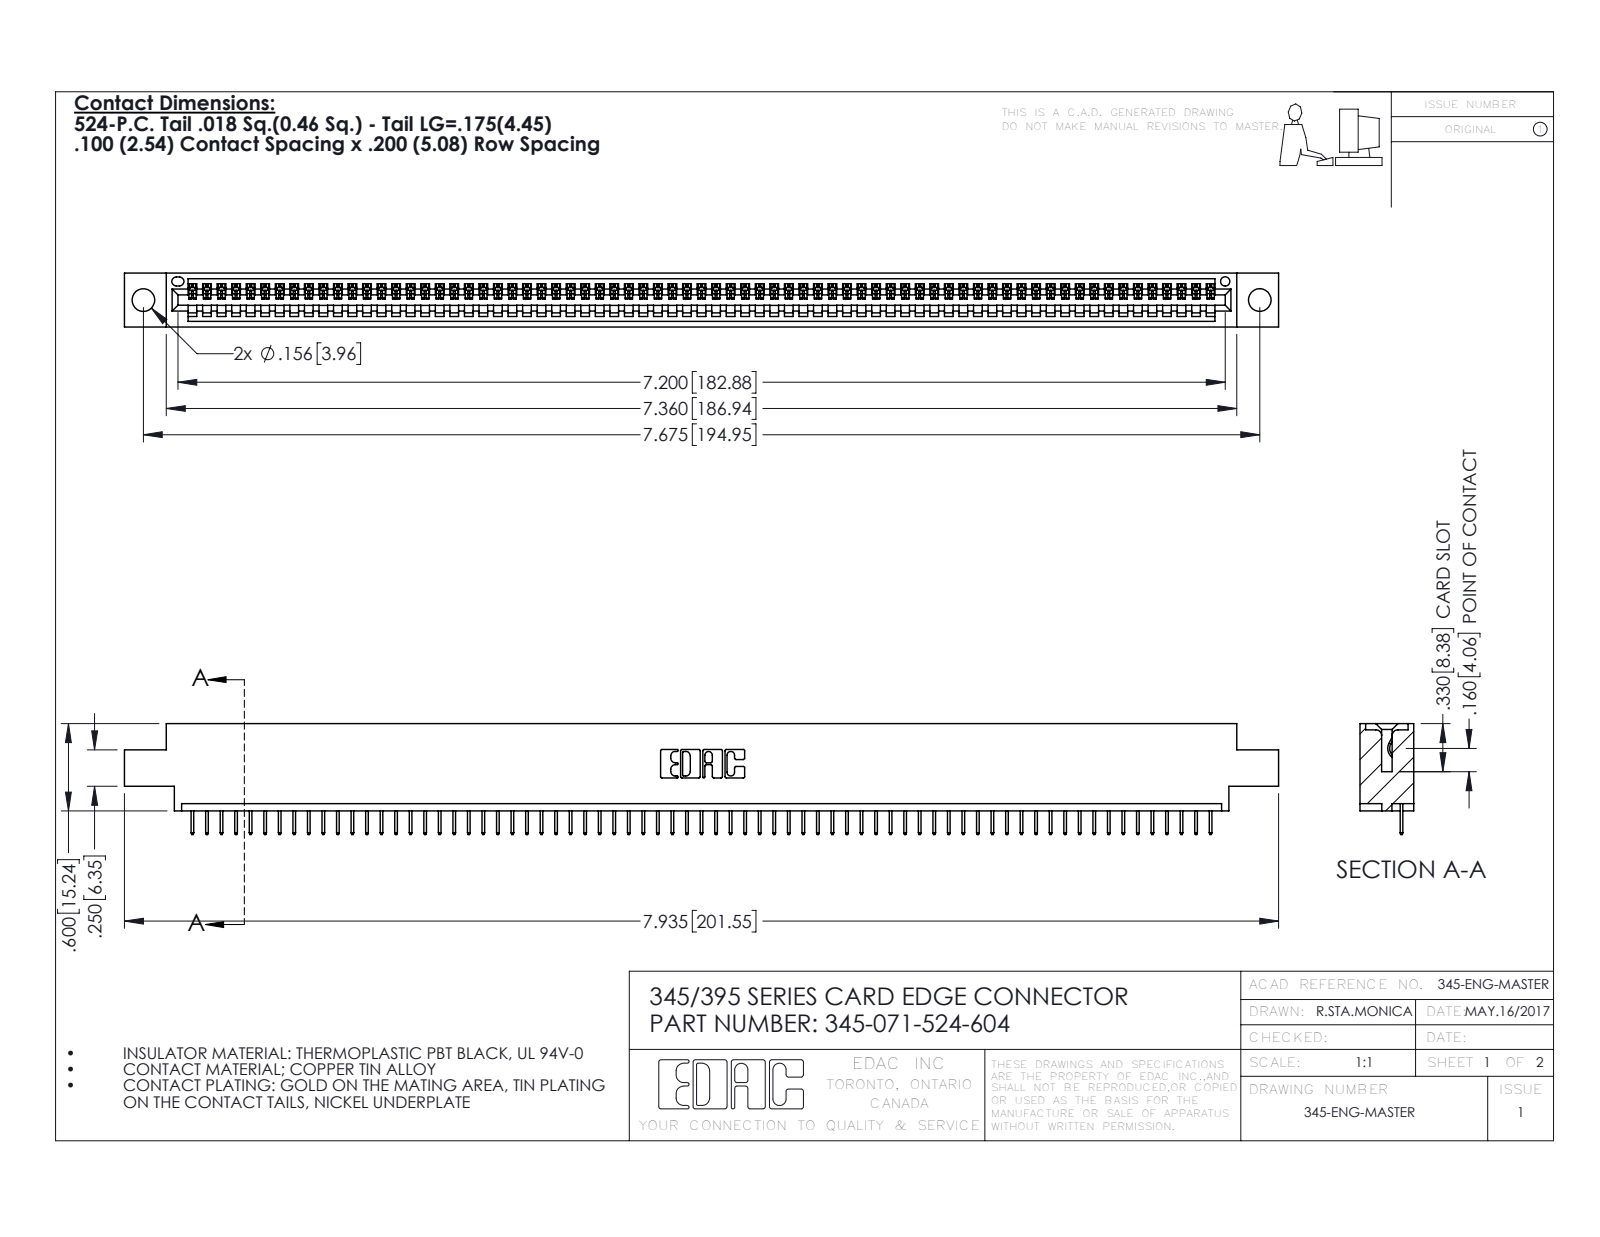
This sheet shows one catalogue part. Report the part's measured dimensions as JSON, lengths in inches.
{"part_name": "345-071-524-604; 345-292-001_345-293-124; 345 Part_0.170 Offset - 0.156 Dia-TH", "step_written_by": "SolidWorks 2016 (CONFIG_CONTROL_DESIGN)", "units": "inches", "bodies": {"solids": 72, "faces": 4532, "planar": 3350, "cylindrical": 1182, "other": 0}, "overall_size": [7.935, 0.762, 0.37], "volume_in3": 1.153, "surface_area_in2": 38.05, "round_holes": [[0.156, 2], [0.064, 1]], "partial_cylinders_radius": [[0.006, 142], [0.01, 22], [0.007, 6], [0.031, 6], [0.026, 3], [0.031, 2], [0.04, 2], [0.014, 1]], "face_to_face_distances": [0.072, 0.298, 0.37, 0.2, 0.098, 0.272, 0.025, 0.225, 0.072, 0.175], "hole_center_spacings": [0.27, 7.439, 7.675]}
